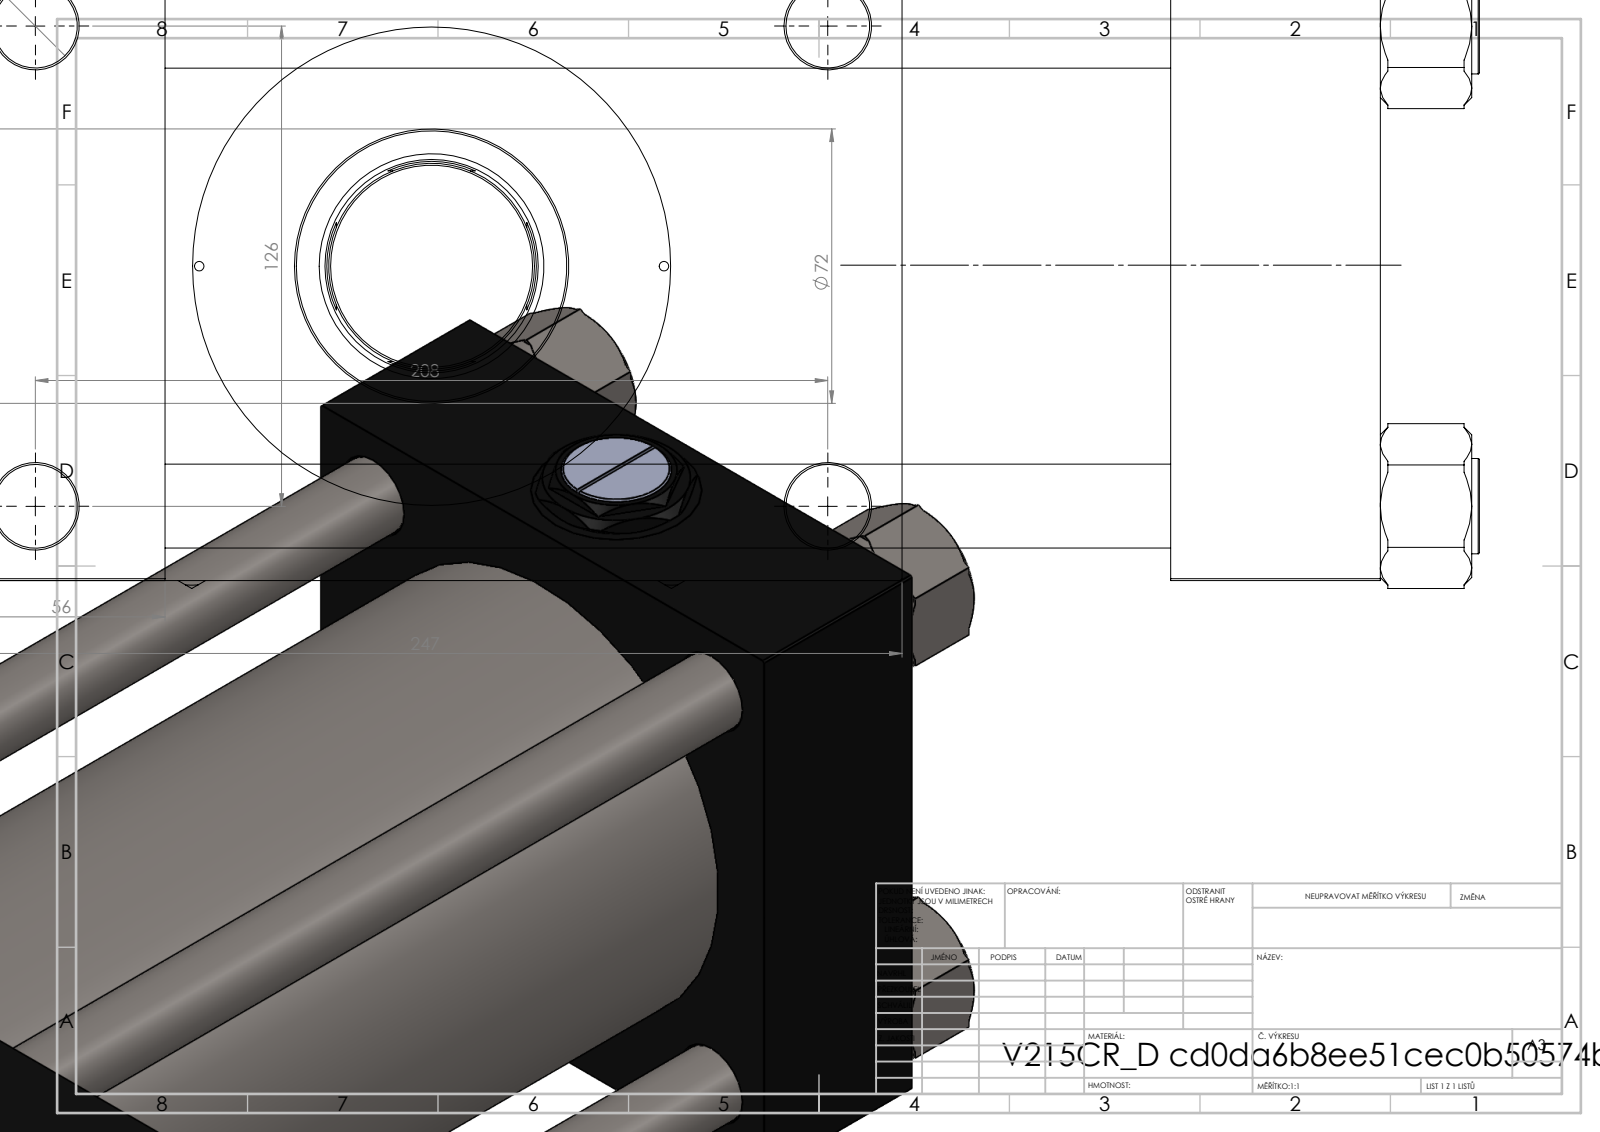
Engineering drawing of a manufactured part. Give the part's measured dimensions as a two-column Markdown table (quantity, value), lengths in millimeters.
| quantity | value |
| --- | --- |
| part name | Zatka_pro_OIL_PORT; V215CR_ROD_END_F; V215CR_D_TYCINKA; V215CR_VCP_D (+3 more) |
| STEP written by | SolidWorks 2019 (CONFIG_CONTROL_DESIGN) |
| units | millimeters |
| bodies | 14 solids, 1269 faces (598 planar, 105 cylindrical, 566 other) |
| overall size | 510 × 247 × 174.07 |
| volume | 5 928 000 mm³ |
| surface area | 783 149 mm² |
| round holes (diameter × count) | 22 × 8, 32.24 × 4, 45 × 4, 7 × 3, 2.5 × 2, 40.5 × 1, 56 × 1, 59 × 1, 96 × 1, 125 × 1, 125.5 × 1 |
| round bosses / shafts (diameter × count) | 25 × 4, 131 × 1, 72 × 1, 54 × 1, 40 × 1 |
| main face-to-face distances | 165, 264, 55, 319, 56, 375, 320, 41, 206, 353.74 |
| hole center spacings | 41.05, 62.98, 76.28, 89.02, 121.59, 125.9, 132.47, 139.02 |
